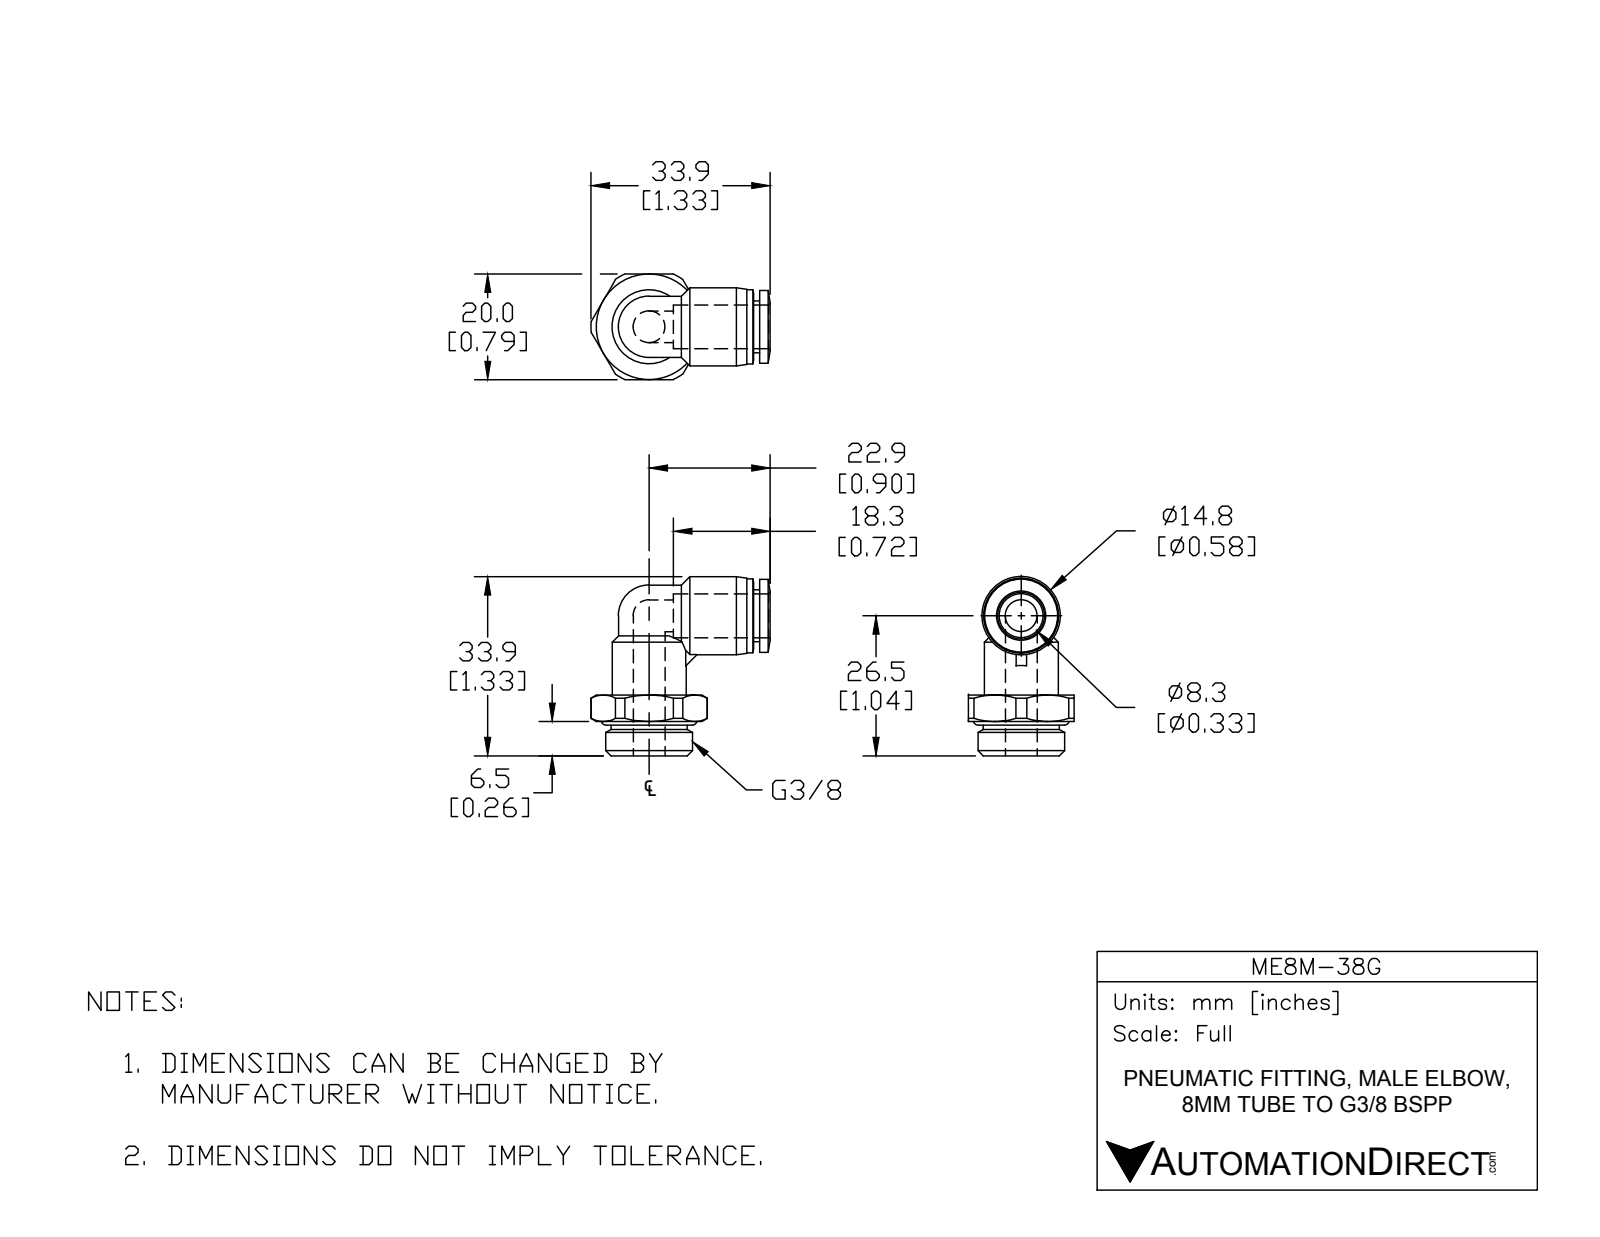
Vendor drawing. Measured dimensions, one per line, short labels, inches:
name: ME8M-38G
written by: SolidWorks 2018 (AUTOMOTIVE_DESIGN)
unit: in
bodies: 2 solids, 84 faces (18 planar, 29 cylindrical, 37 other)
size: 1.335 × 1.335 × 0.787
volume: 0.394 in³; area: 6.912 in²
holes: 2× ⌀0.236, 1× ⌀0.327
bosses: 2× ⌀0.551, 1× ⌀0.646, 1× ⌀0.583, 1× ⌀0.567, 1× ⌀0.543, 1× ⌀0.457, 1× ⌀0.386
rounds: 1× R0.228, 1× R0.433
face distances: 0.453, 0.787, 0.045, 0.256, 0.197, 0.303, 0.047, 0.15, 0.596, 0.642
